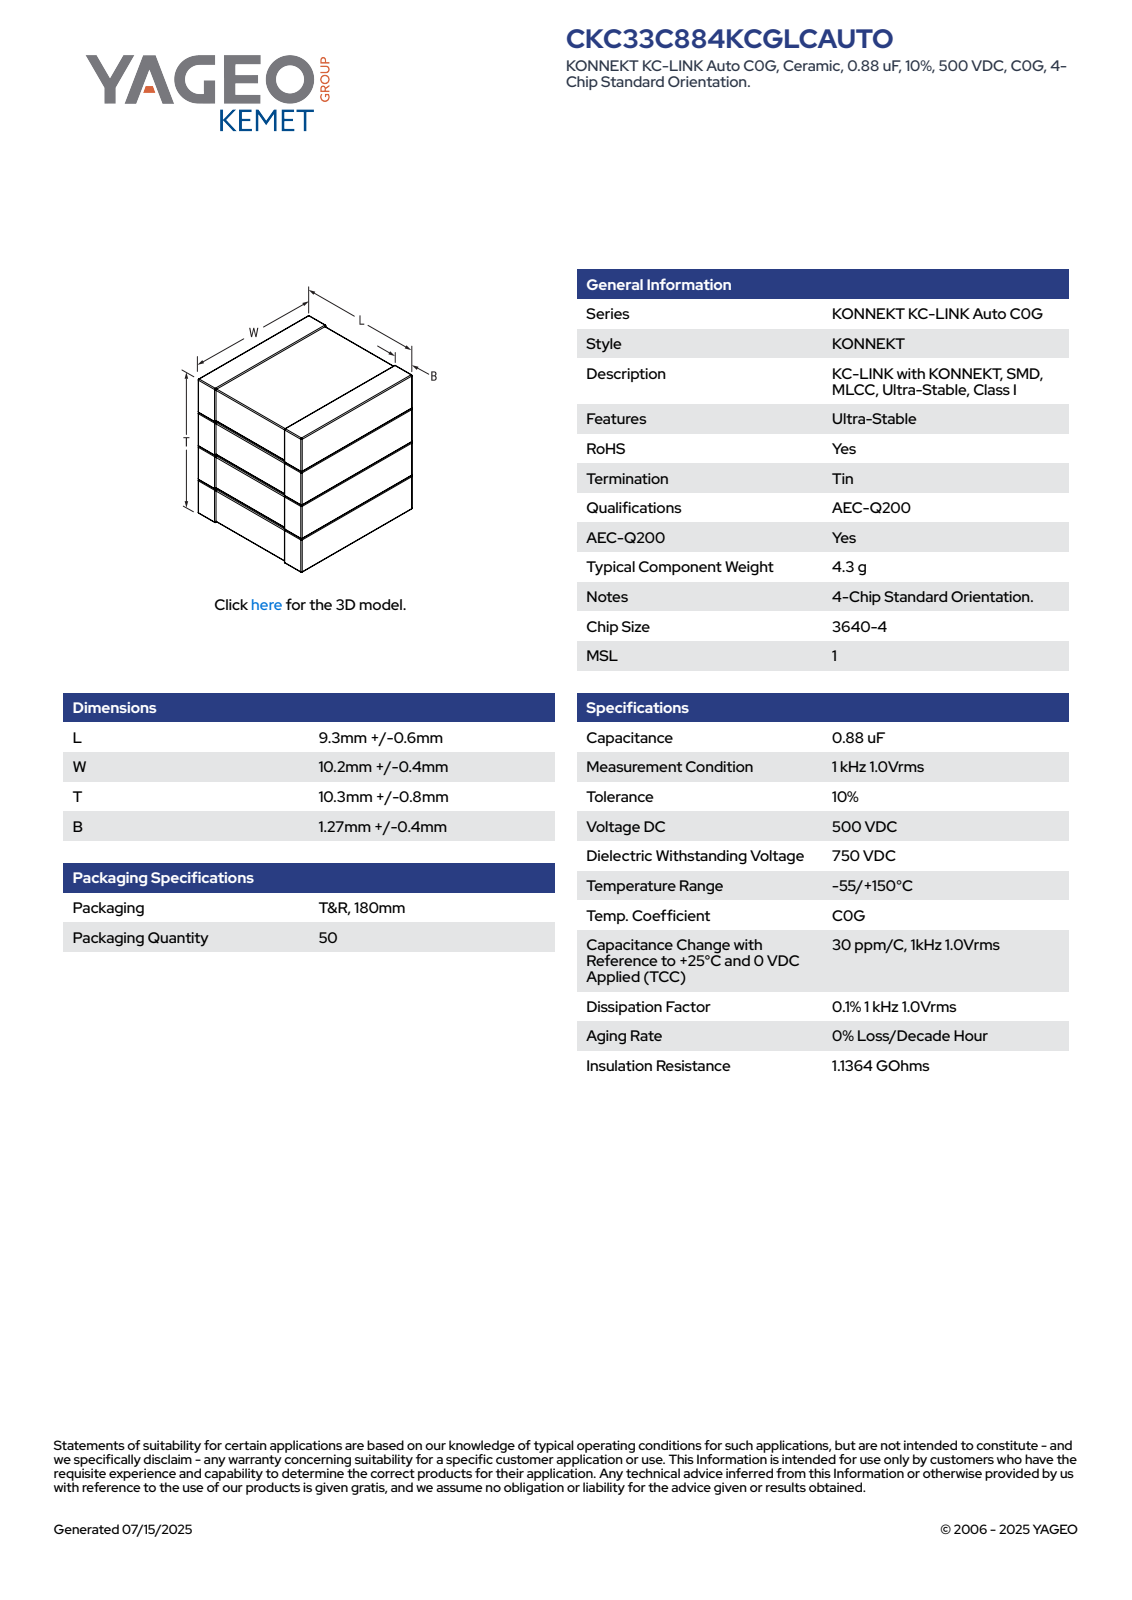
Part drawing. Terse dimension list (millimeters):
name: CCSS_K4T_3640_L9.9W10.6B1.67T11.1
written by: SolidWorks 2020 (AUTOMOTIVE_DESIGN)
unit: mm
bodies: 5 solids, 321 faces (105 planar, 152 cylindrical, 64 other)
size: 11.1 × 10.6 × 9.9
volume: 1 116 mm³; area: 1 159 mm²
face distances: 2.78, 5.55, 5.48, 5.56, 2.64, 2.63, 2.77, 5.41, 8.19, 8.33
